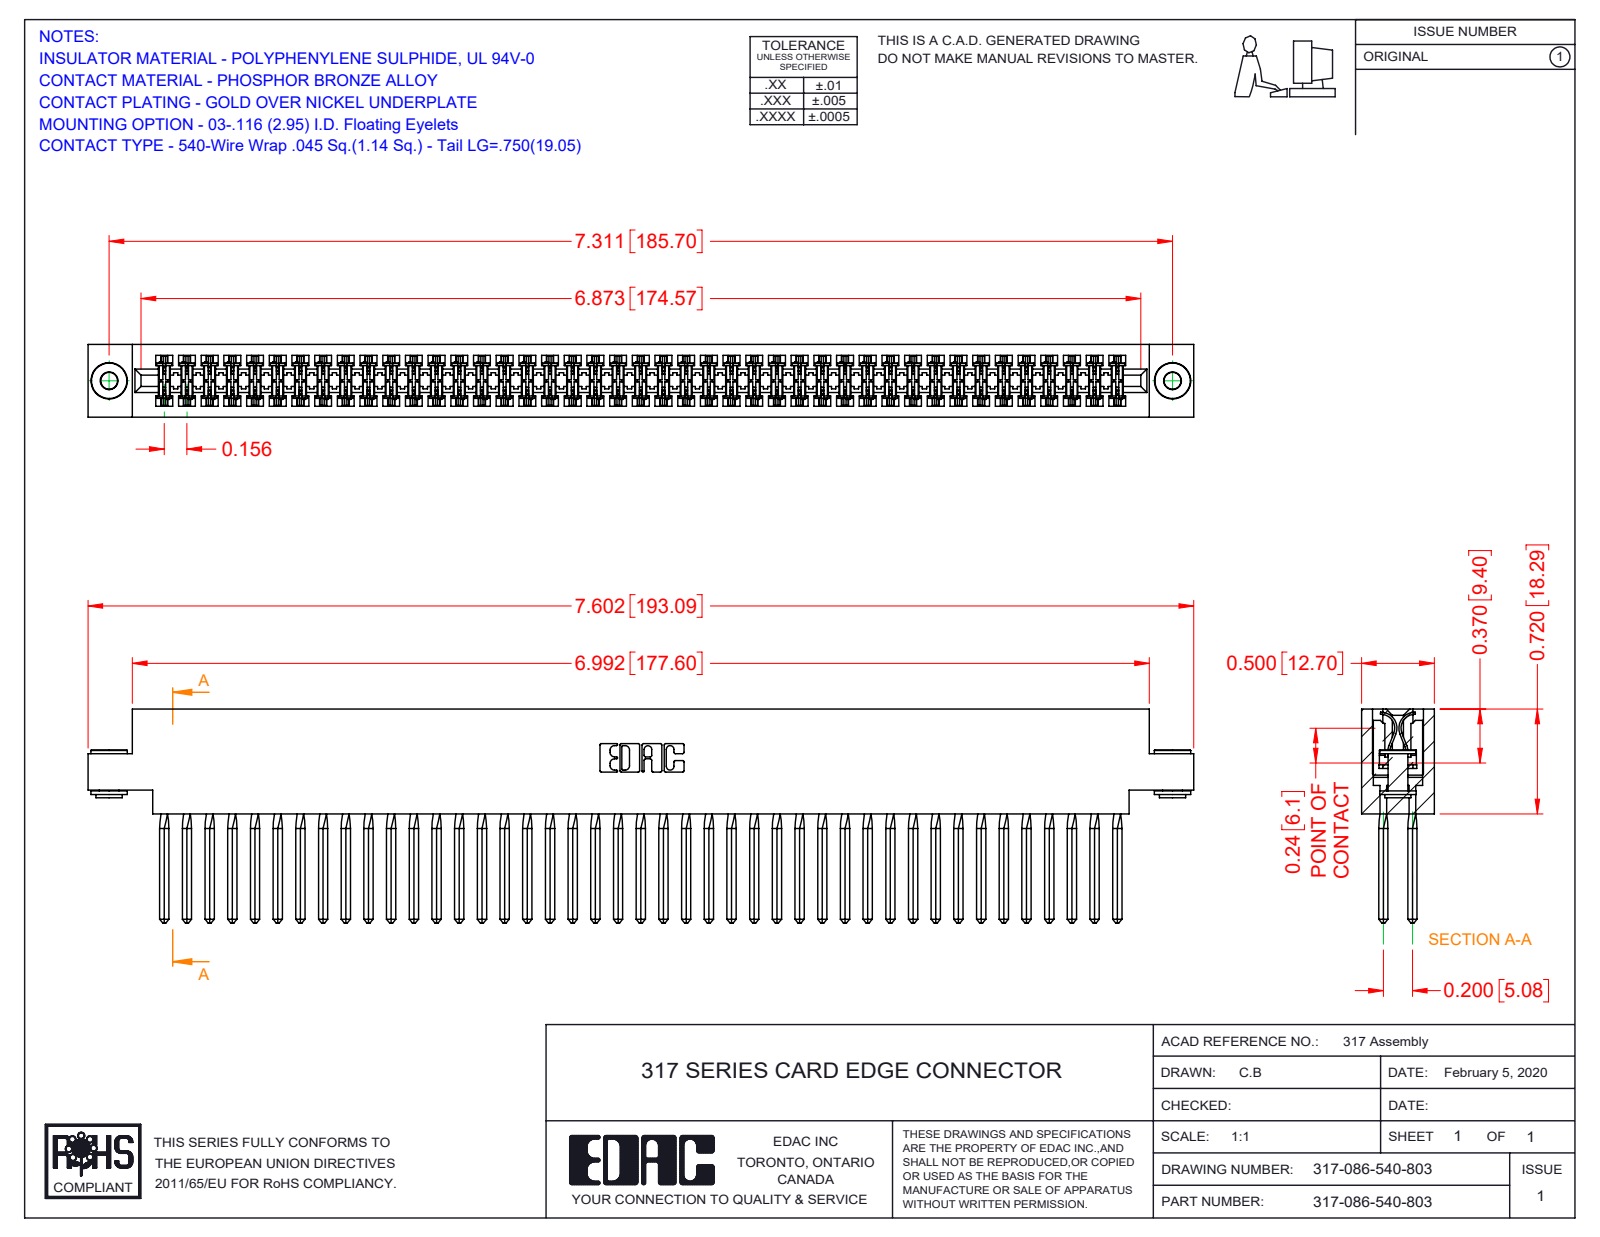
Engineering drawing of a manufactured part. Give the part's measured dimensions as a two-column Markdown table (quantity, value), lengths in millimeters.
| quantity | value |
| --- | --- |
| part name | 317 Part_.156 Dia - TH; 317-086-540-803; 317-290-001_540; 345-250-002_345-250-002-102 |
| STEP written by | SolidWorks 2016 (CONFIG_CONTROL_DESIGN) |
| units | millimeters |
| bodies | 89 solids, 7794 faces (6346 planar, 1096 cylindrical, 352 other) |
| overall size | 193.1 × 37.3 × 12.7 |
| volume | 32 460 mm³ |
| surface area | 48 650 mm² |
| round holes (diameter × count) | 2.9 × 2, 4 × 2 |
| round bosses / shafts (diameter × count) | 6.4 × 2, 4.6 × 2, 3.5 × 2 |
| partial cylindrical surfaces (radius × count) | 0.4 × 172, 0.3 × 22, 0.2 × 6, 0.8 × 6, 0.7 × 3, 2.4 × 2, 2.5 × 2, 2.8 × 2 |
| main face-to-face distances | 12.7, 1.9, 10.8, 8.9, 5, 2.4, 5.1, 2.9, 3.3, 1.2 |
| hole center spacings | 185.7 |
